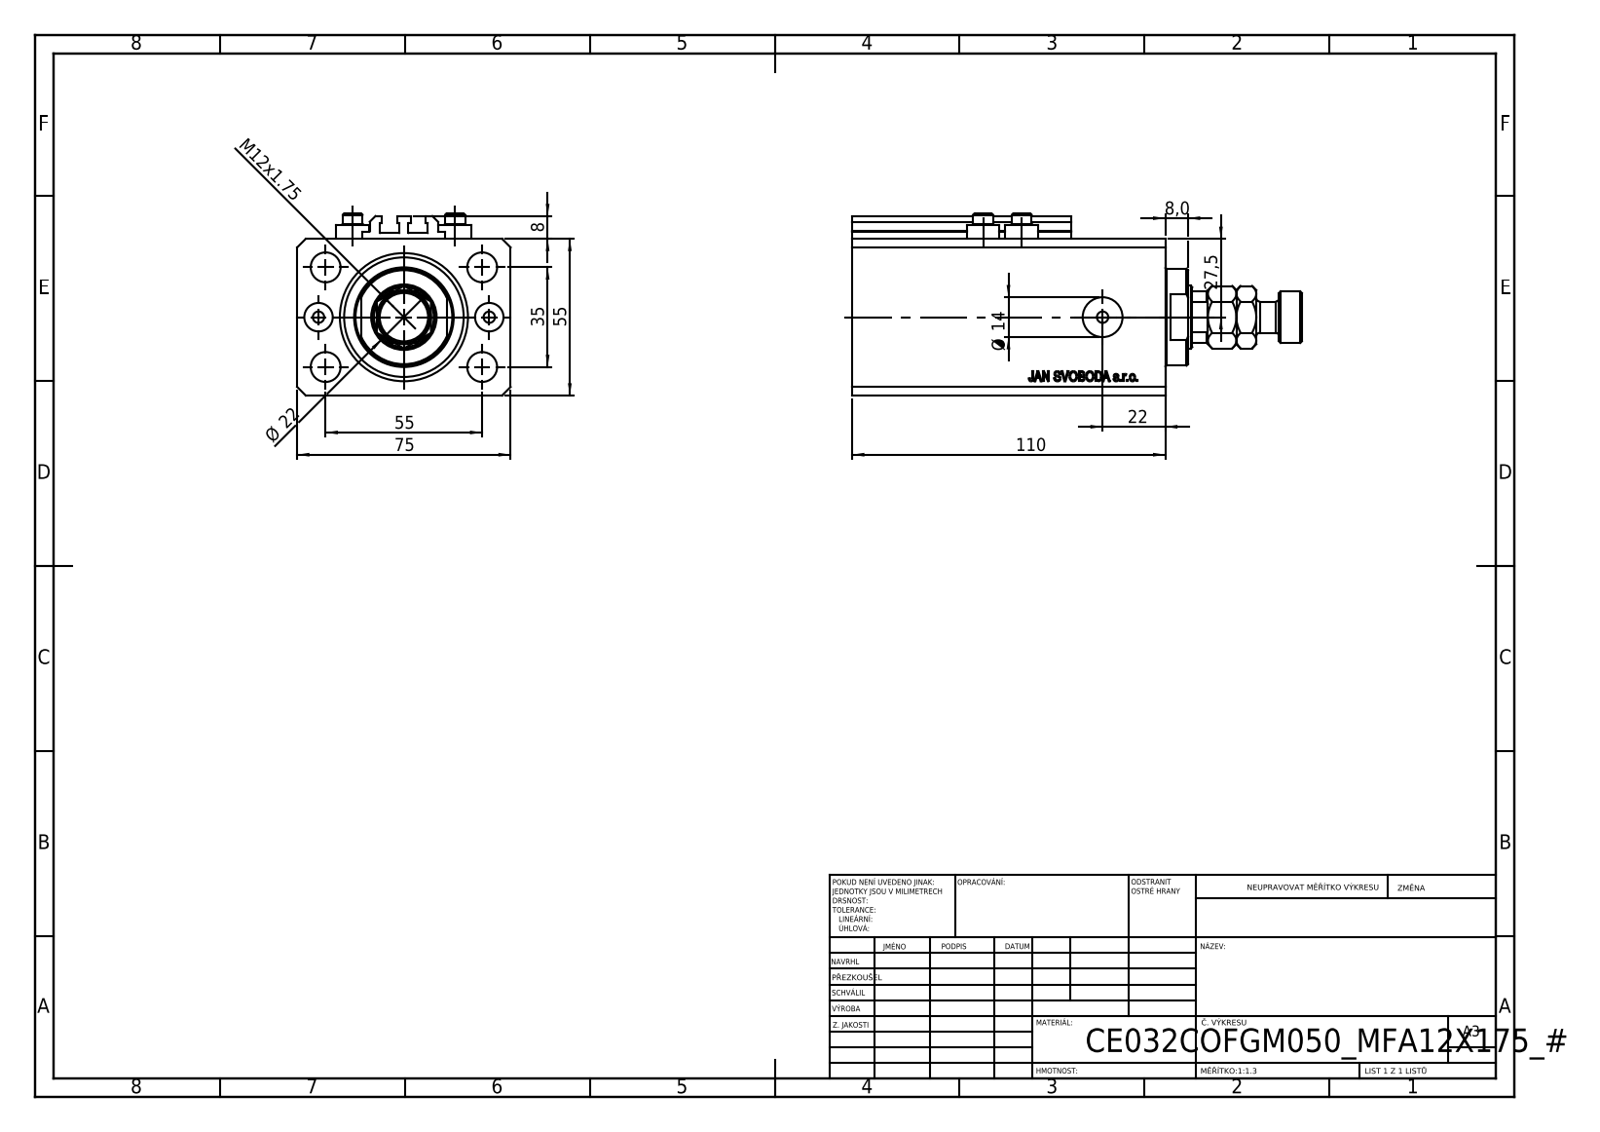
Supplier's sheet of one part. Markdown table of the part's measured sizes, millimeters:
| quantity | value |
| --- | --- |
| part name | V250CE_C_VCP; V250CE_C_Body; V250CE_VC_C; ALLEN BOLT V250CE (+1 more) |
| STEP written by | SolidWorks 2019 (CONFIG_CONTROL_DESIGN) |
| units | millimeters |
| bodies | 9 solids, 1086 faces (520 planar, 90 cylindrical, 476 other) |
| overall size | 158 × 75 × 64 |
| volume | 416 999 mm³ |
| surface area | 93 814 mm² |
| round holes (diameter × count) | 4 × 8, 10.5 × 5, 10 × 2, 14 × 2, 22 × 1, 32 × 1, 45 × 1 |
| round bosses / shafts (diameter × count) | 11.6 × 4, 7 × 4, 34 × 1, 18 × 1, 11 × 1 |
| partial cylindrical surfaces (radius × count) | 0.2 × 10, 10.5 × 1 |
| main face-to-face distances | 55, 75, 15, 110, 95, 9.9, 85.1, 100.1, 2.5, 8 |
| hole center spacings | 17.68, 32.6, 60.1, 13.6, 30, 35, 36, 38.48 |
